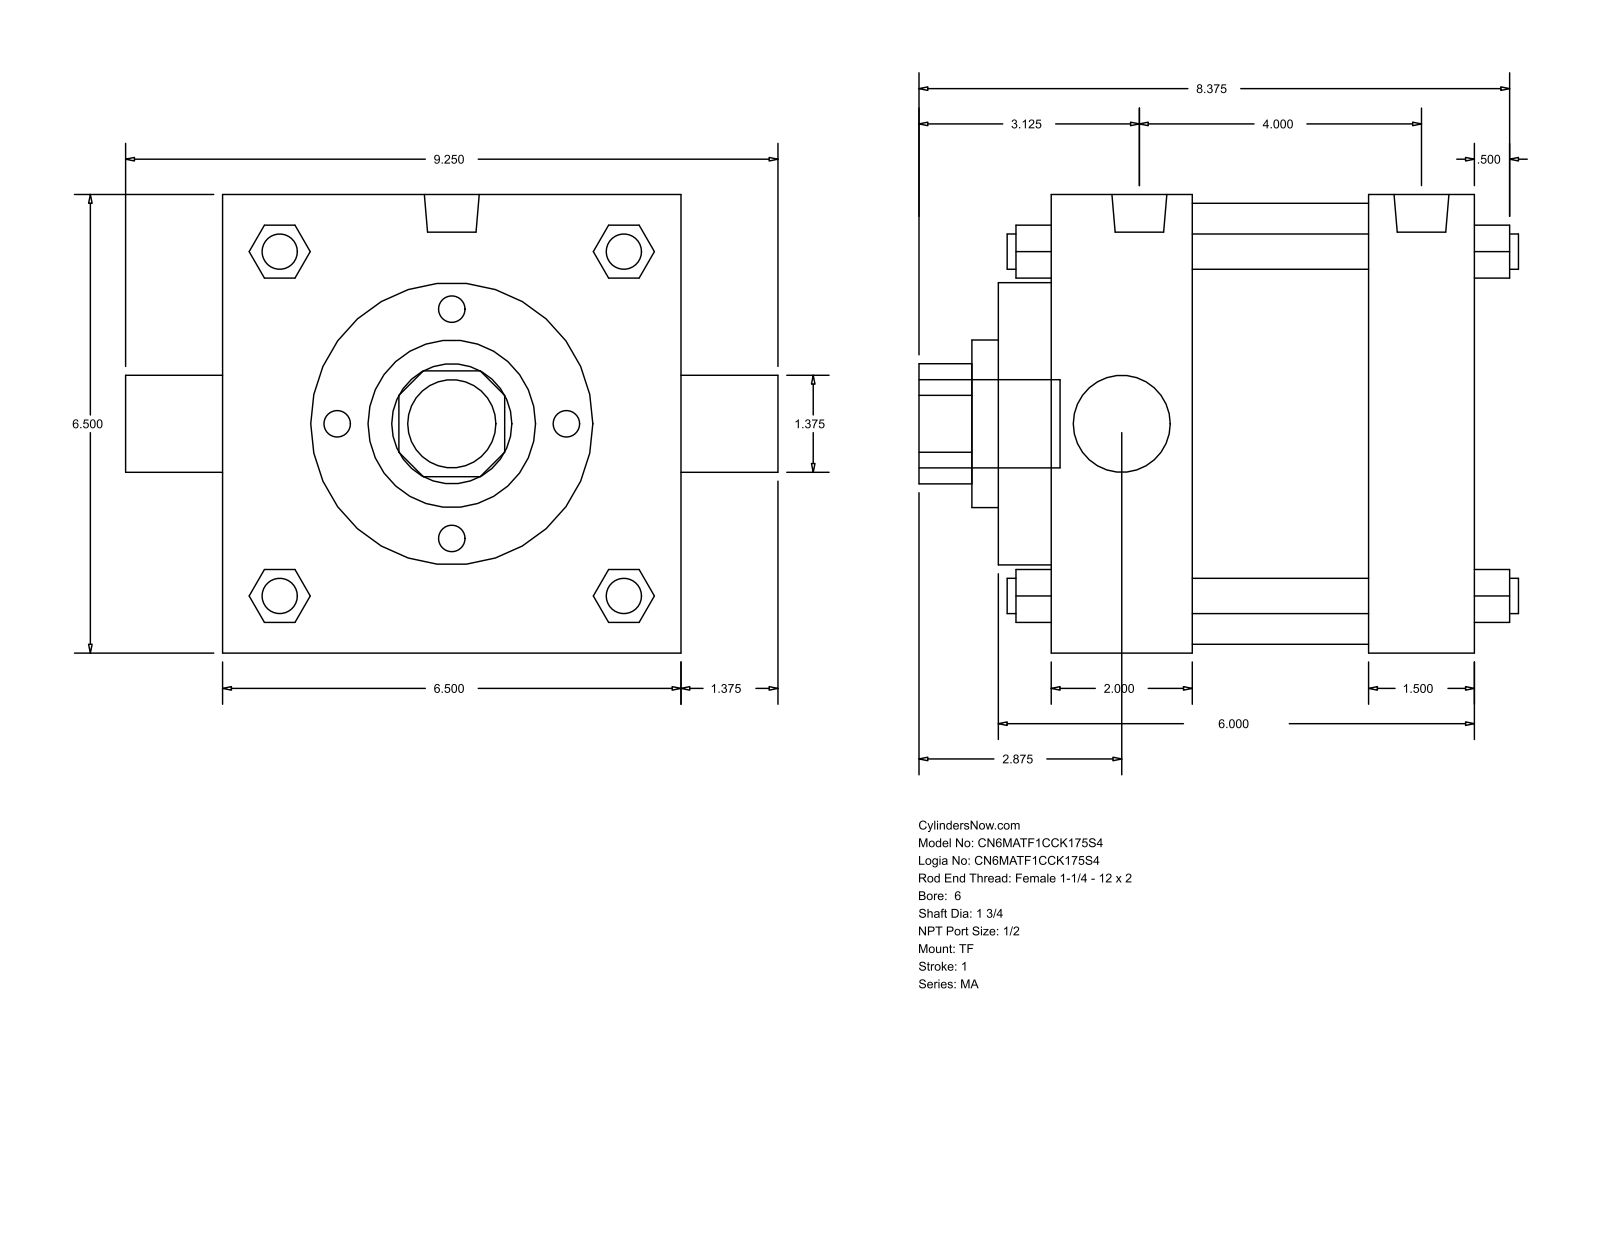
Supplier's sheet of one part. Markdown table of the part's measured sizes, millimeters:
| quantity | value |
| --- | --- |
| part name | MA_TF__0600_1.75 |
| STEP written by | GSSL Pune (CONFIG_CONTROL_DESIGN) |
| units | millimeters |
| bodies | 0 solids, 122 faces (93 planar, 29 cylindrical, 0 other) |
| overall size | 234.95 × 215.9 × 165.1 |
| round holes (diameter × count) | 34.92 × 1, 44.45 × 1, 60.33 × 1, 101.6 × 1, 158.75 × 1 |
| round bosses / shafts (diameter × count) | 12.7 × 4, 17.46 × 3, 19.77 × 2, 31.75 × 1 |
| partial cylindrical surfaces (radius × count) | 21.63 × 1 |
| main face-to-face distances | 165.1, 152.41, 19.05, 38.1, 50.8, 101.61, 114.31, 63.51, 69.85, 133.36 |
